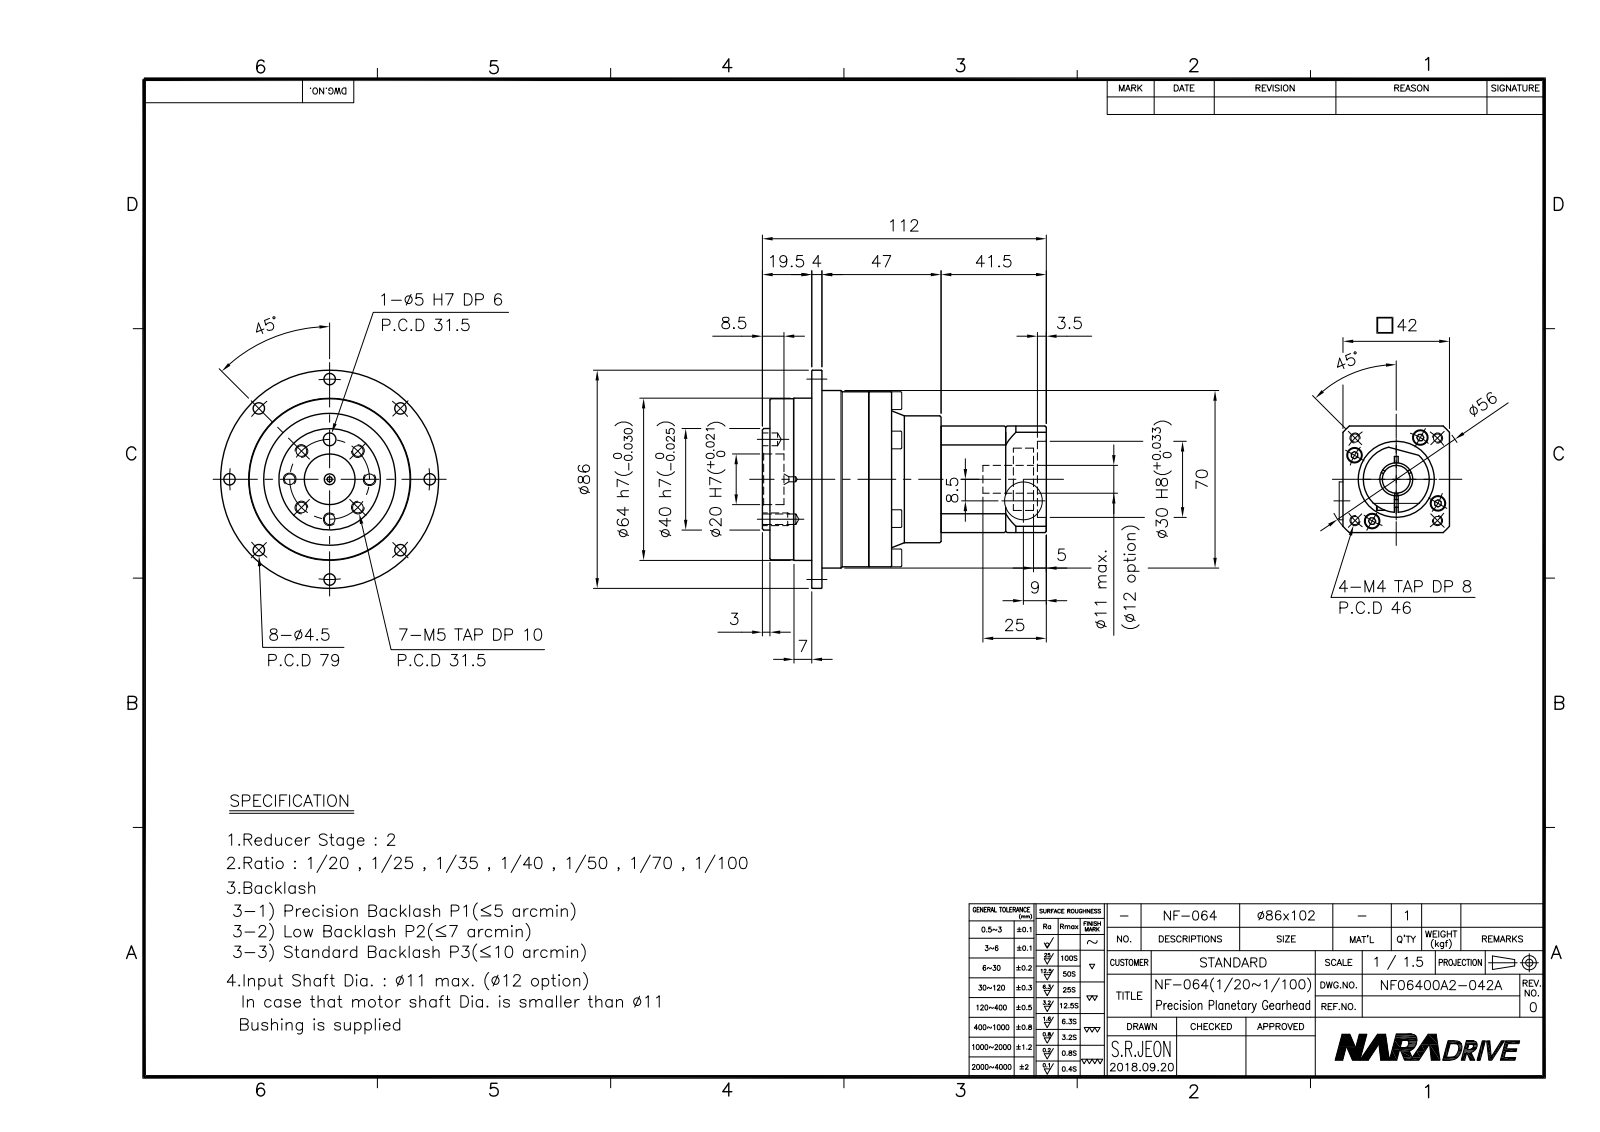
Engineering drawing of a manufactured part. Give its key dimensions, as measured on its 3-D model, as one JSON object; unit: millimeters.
{"part_name": "NF06400A2-042A", "step_written_by": "Autodesk Inventor 2016 (AUTOMOTIVE_DESIGN)", "units": "millimeters", "bodies": {"solids": 2, "faces": 438, "planar": 204, "cylindrical": 117, "other": 117}, "overall_size": [112, 86, 86], "volume_mm3": 212144, "surface_area_mm2": 62902, "round_holes": [[4.5, 14], [3.24, 10], [3.4, 9], [6, 8], [4.13, 7], [2.46, 5], [2, 1], [5, 1], [7, 1], [8.5, 1], [11, 1], [13, 1]], "round_bosses_or_shafts": [[5.5, 11], [3, 11], [86, 1], [70, 1], [69, 1], [64, 1], [63.5, 1], [50, 1]], "partial_cylinders_radius": [[3, 1], [28, 1]], "face_to_face_distances": [19.5, 42, 22.5, 3, 28.5, 48, 4, 18.5, 8, 51], "hole_center_spacings": [30.47, 42.52, 51.85, 12.06, 15.75, 29.11, 30.23, 39.5]}
